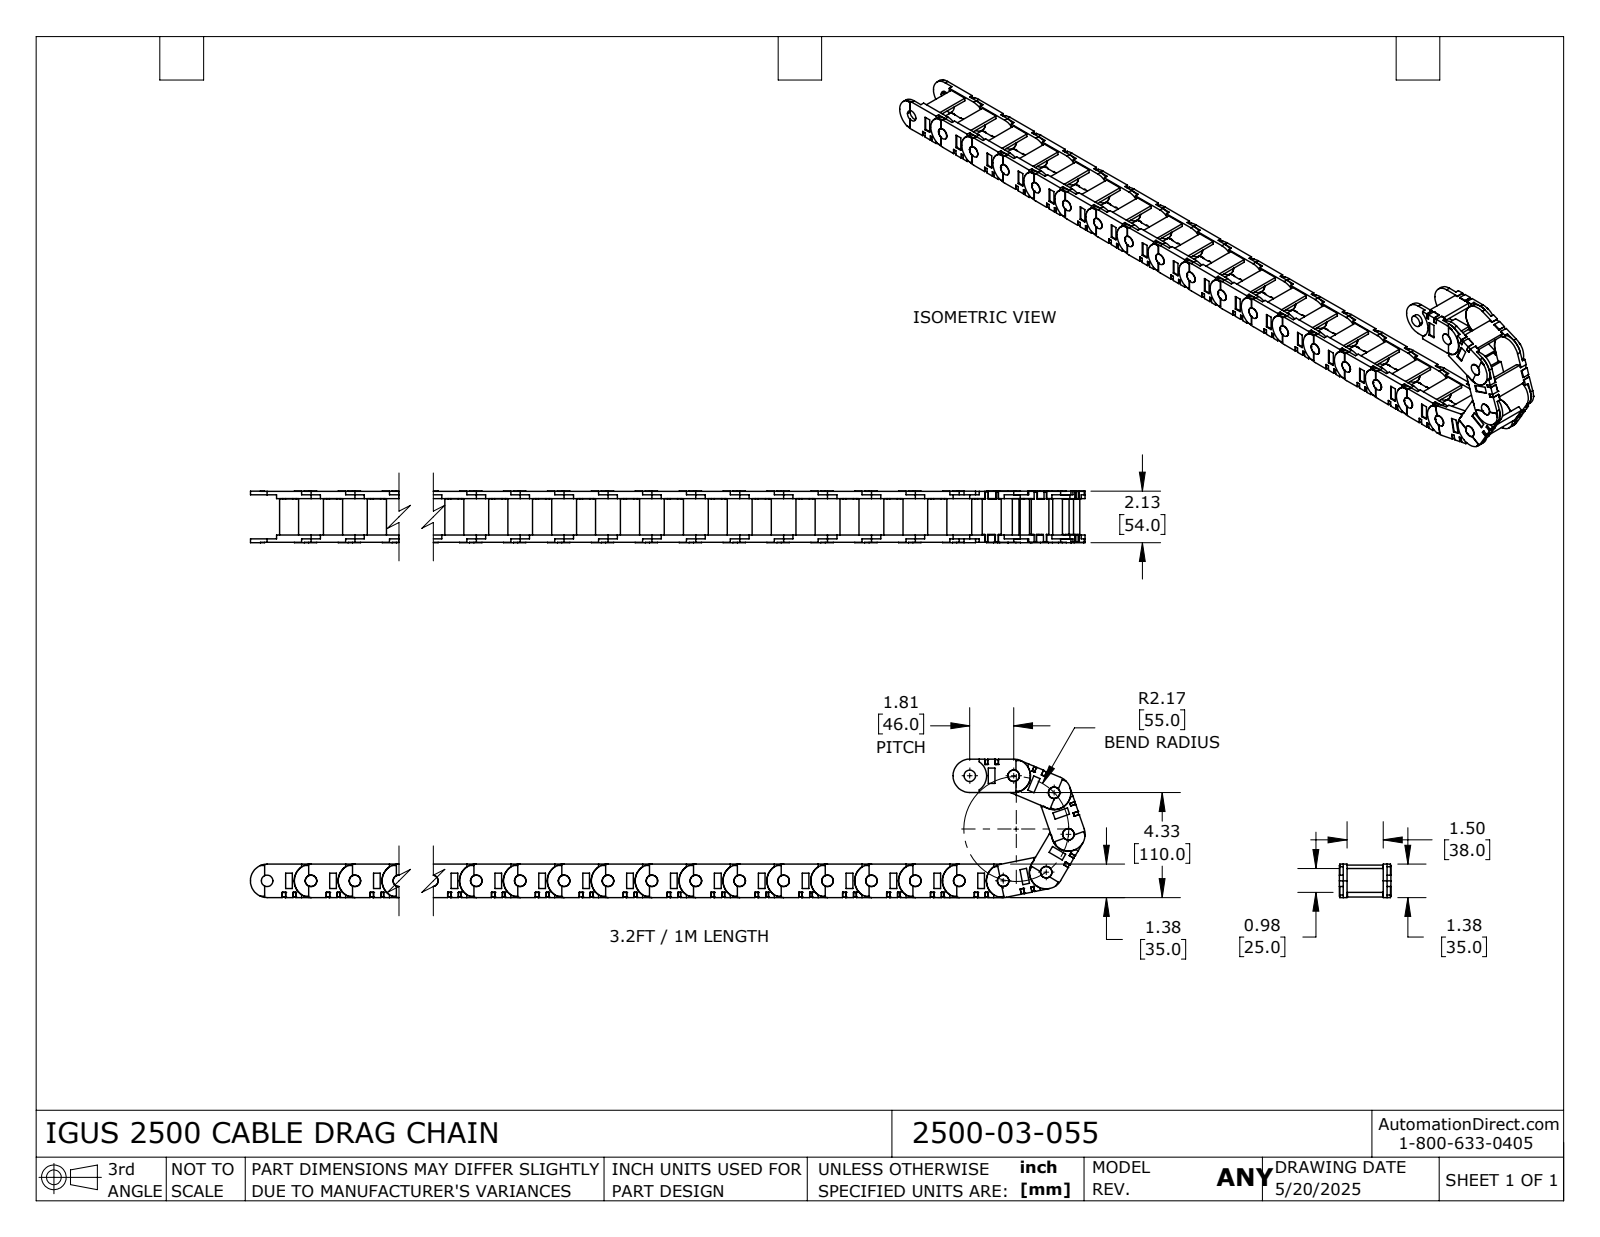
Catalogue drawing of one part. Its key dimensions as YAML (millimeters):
part_name: "2500_03_055"
step_written_by: "SolidWorks 2024 (AUTOMOTIVE_DESIGN)"
units: millimeters
bodies: {solids: 66, faces: 2398, planar: 1870, cylindrical: 528, other: 0}
overall_size: [885.4, 145, 54]
volume: 670100
surface_area: 387900
round_holes:
  - {diameter: 12, count: 22}
round_bosses_or_shafts:
  - {diameter: 12, count: 22}
  - {diameter: 35, count: 21}
partial_cylinders:
  - {radius: 17.7, count: 23}
  - {radius: 17.5, count: 2}
face_to_face_distances: [4, 42, 46, 3.6, 7.6, 45.6, 49.6, 38, 0.4, 53.2]
hole_center_spacings: [46, 92, 138, 184, 230, 276, 322, 368]
